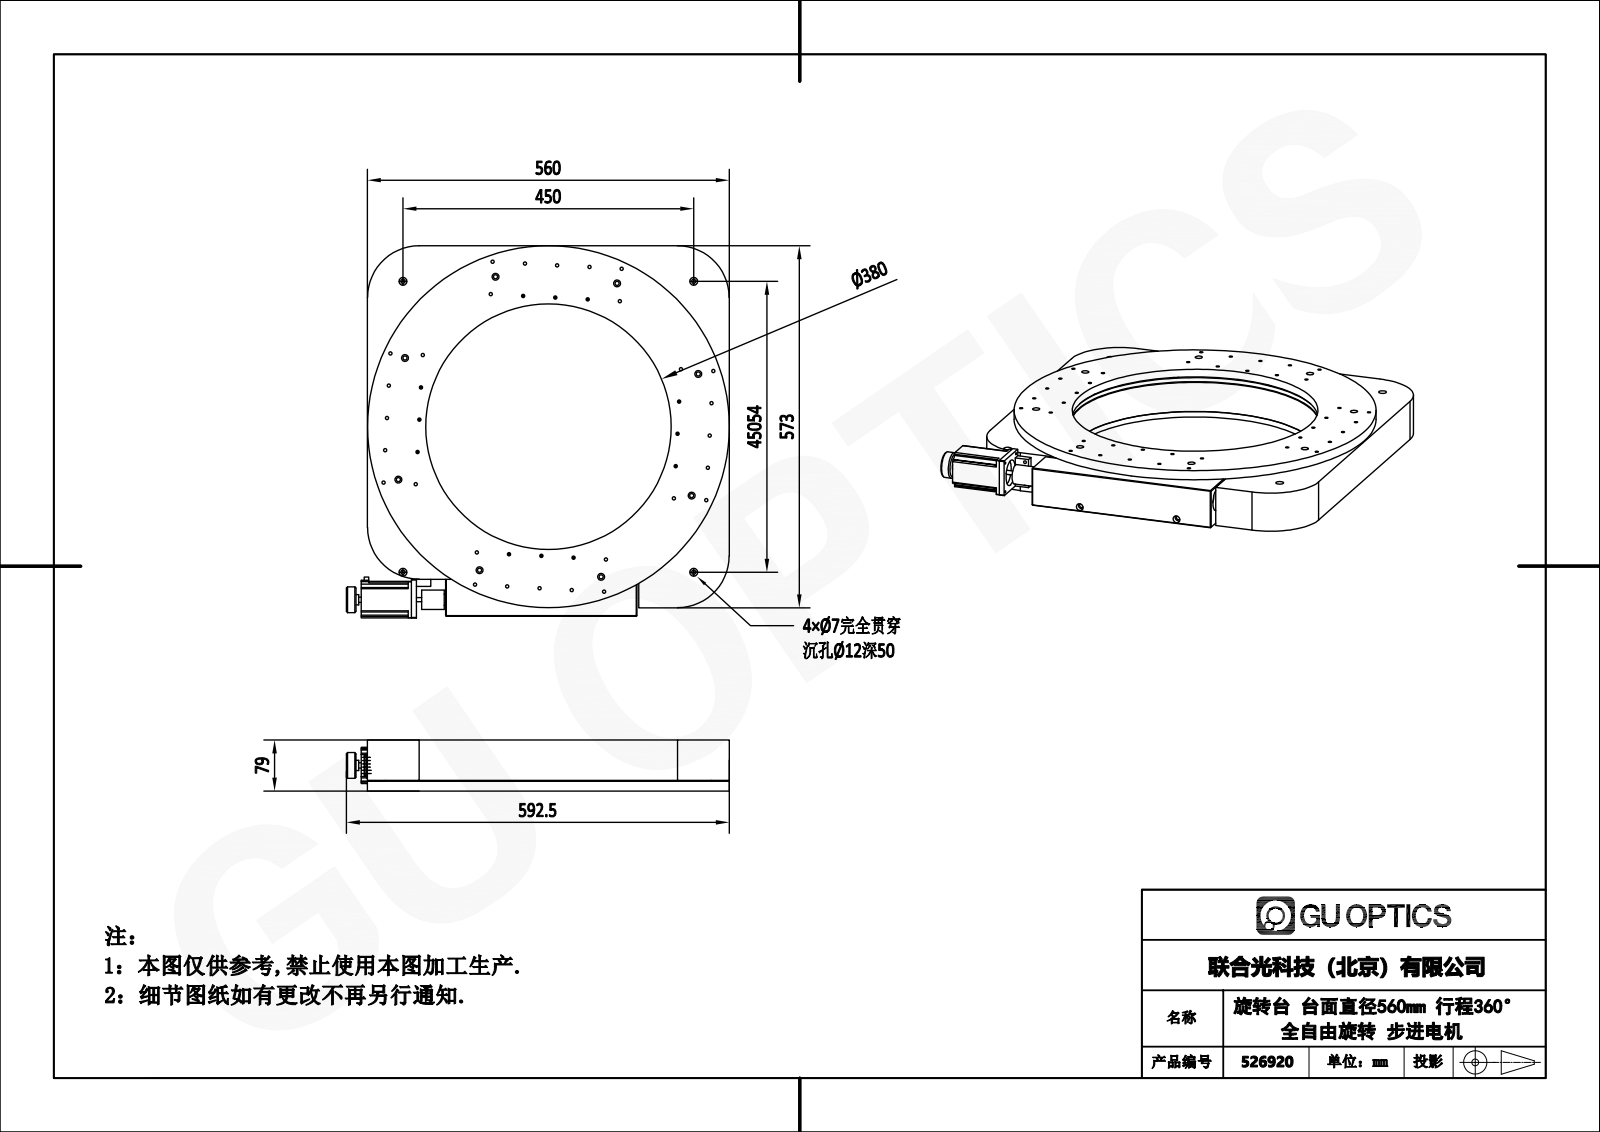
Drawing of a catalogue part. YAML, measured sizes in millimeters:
part_name: "FMSR560"
step_written_by: "SolidWorks 2017 (AUTOMOTIVE_DESIGN)"
units: millimeters
bodies: {solids: 14, faces: 754, planar: 158, cylindrical: 448, other: 148}
overall_size: [592.5, 576, 79]
volume: 12050000
surface_area: 1826000
round_holes:
  - {diameter: 5, count: 66}
  - {diameter: 3.3, count: 28}
  - {diameter: 8, count: 16}
  - {diameter: 7, count: 12}
  - {diameter: 11, count: 10}
  - {diameter: 4.2, count: 8}
  - {diameter: 6, count: 8}
  - {diameter: 10, count: 8}
  - {diameter: 5.1, count: 4}
  - {diameter: 12, count: 4}
  - {diameter: 4.5, count: 2}
  - {diameter: 6.5, count: 2}
round_bosses_or_shafts:
  - {diameter: 1, count: 6}
  - {diameter: 560, count: 1}
  - {diameter: 512, count: 1}
  - {diameter: 504, count: 1}
  - {diameter: 500, count: 1}
  - {diameter: 430, count: 1}
  - {diameter: 420, count: 1}
  - {diameter: 38, count: 1}
partial_cylinders:
  - {radius: 2, count: 14}
  - {radius: 5, count: 4}
  - {radius: 80, count: 4}
  - {radius: 265, count: 1}
face_to_face_distances: [22, 57, 2, 11, 79, 53.5, 13, 9, 48, 2.5]
hole_center_spacings: [155.1, 286.12, 196.5, 150.78, 158.81, 197, 225.68, 226.74]
